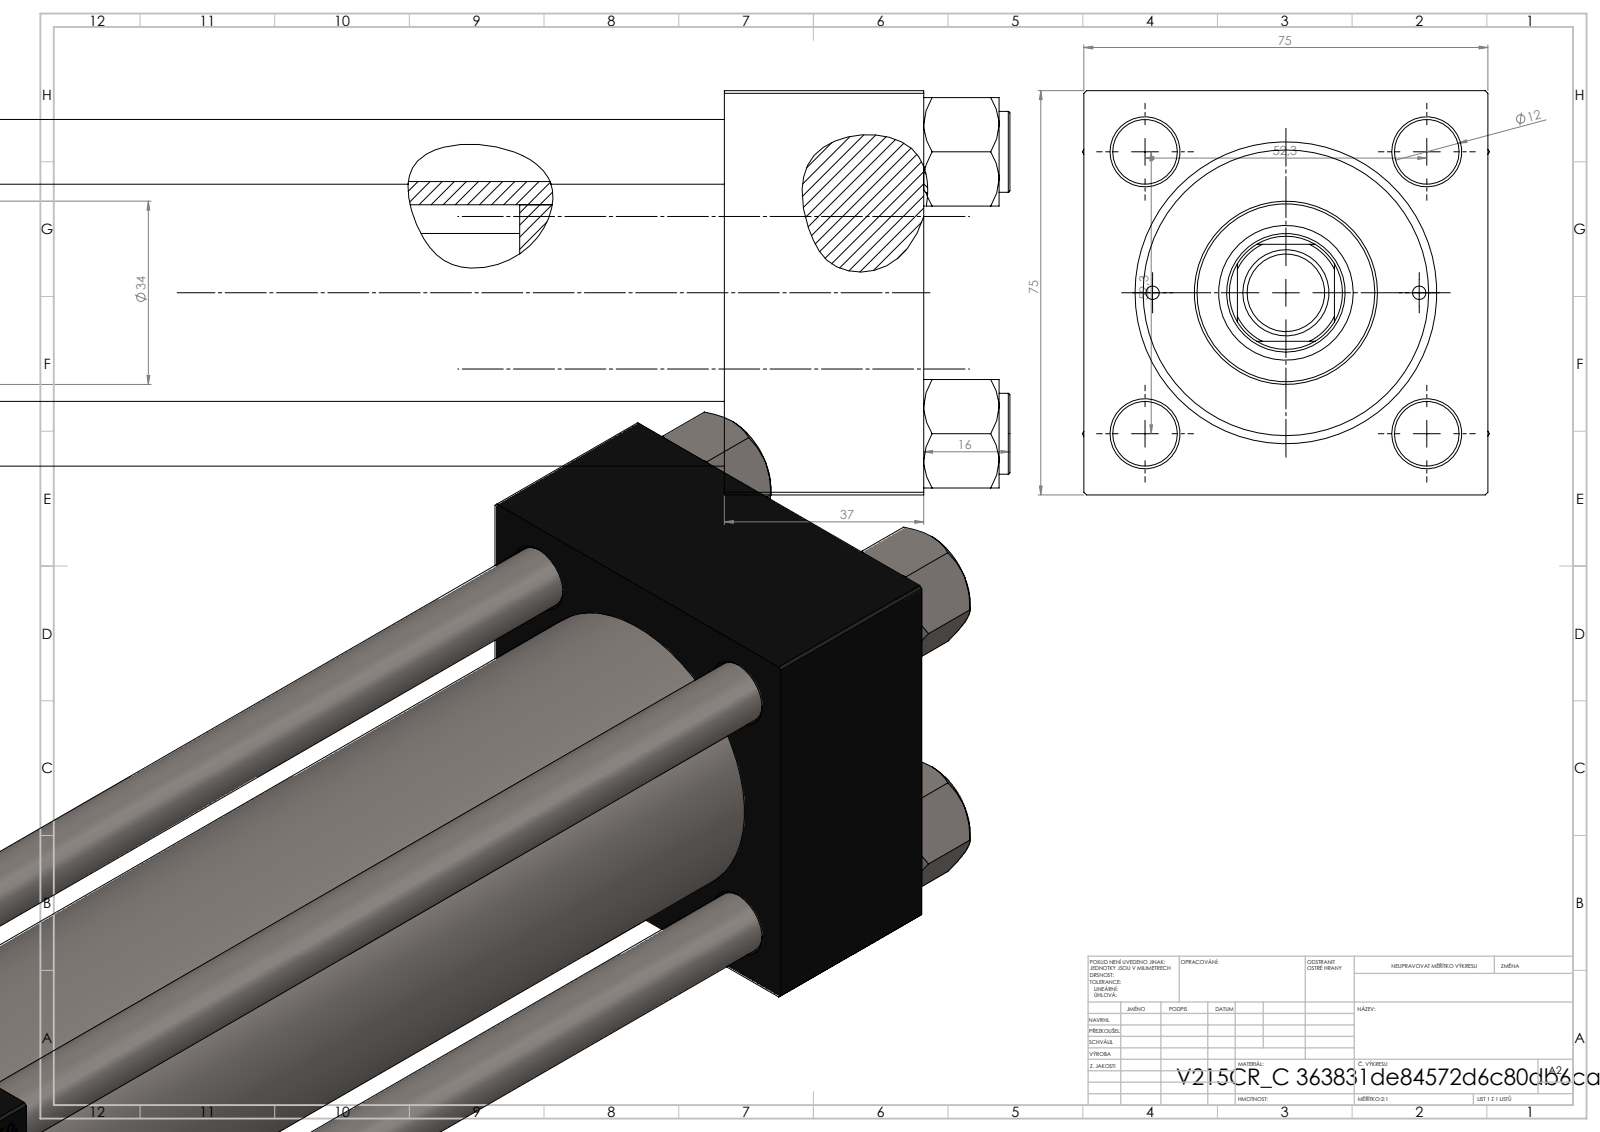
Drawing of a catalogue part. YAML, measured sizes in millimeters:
part_name: "V215CR_C_TYCINKA; V215CR_VCP_C; V215_VC_A; V215CR_C_Body (+2 more)"
step_written_by: "SolidWorks 2019 (CONFIG_CONTROL_DESIGN)"
units: millimeters
bodies: {solids: 12, faces: 1169, planar: 532, cylindrical: 95, other: 542}
overall_size: [357, 75.54, 75]
volume: 847618
surface_area: 226315
round_holes:
  - {diameter: 12, count: 4}
  - {diameter: 2.5, count: 2}
  - {diameter: 7, count: 2}
  - {diameter: 20.96, count: 2}
  - {diameter: 30, count: 2}
  - {diameter: 10.5, count: 1}
  - {diameter: 22, count: 1}
  - {diameter: 25, count: 1}
  - {diameter: 41, count: 1}
  - {diameter: 50, count: 1}
  - {diameter: 53, count: 1}
round_bosses_or_shafts:
  - {diameter: 15, count: 4}
  - {diameter: 56, count: 1}
  - {diameter: 34, count: 1}
  - {diameter: 16, count: 1}
  - {diameter: 14, count: 1}
partial_cylinders:
  - {radius: 10.5, count: 1}
face_to_face_distances: [75, 37, 294, 257, 235, 198, 59, 265.3, 228.3, 30.3]
hole_center_spacings: [26.19, 36.98, 52.3, 57.22, 24.75, 73.96, 49.5, 233.5]
